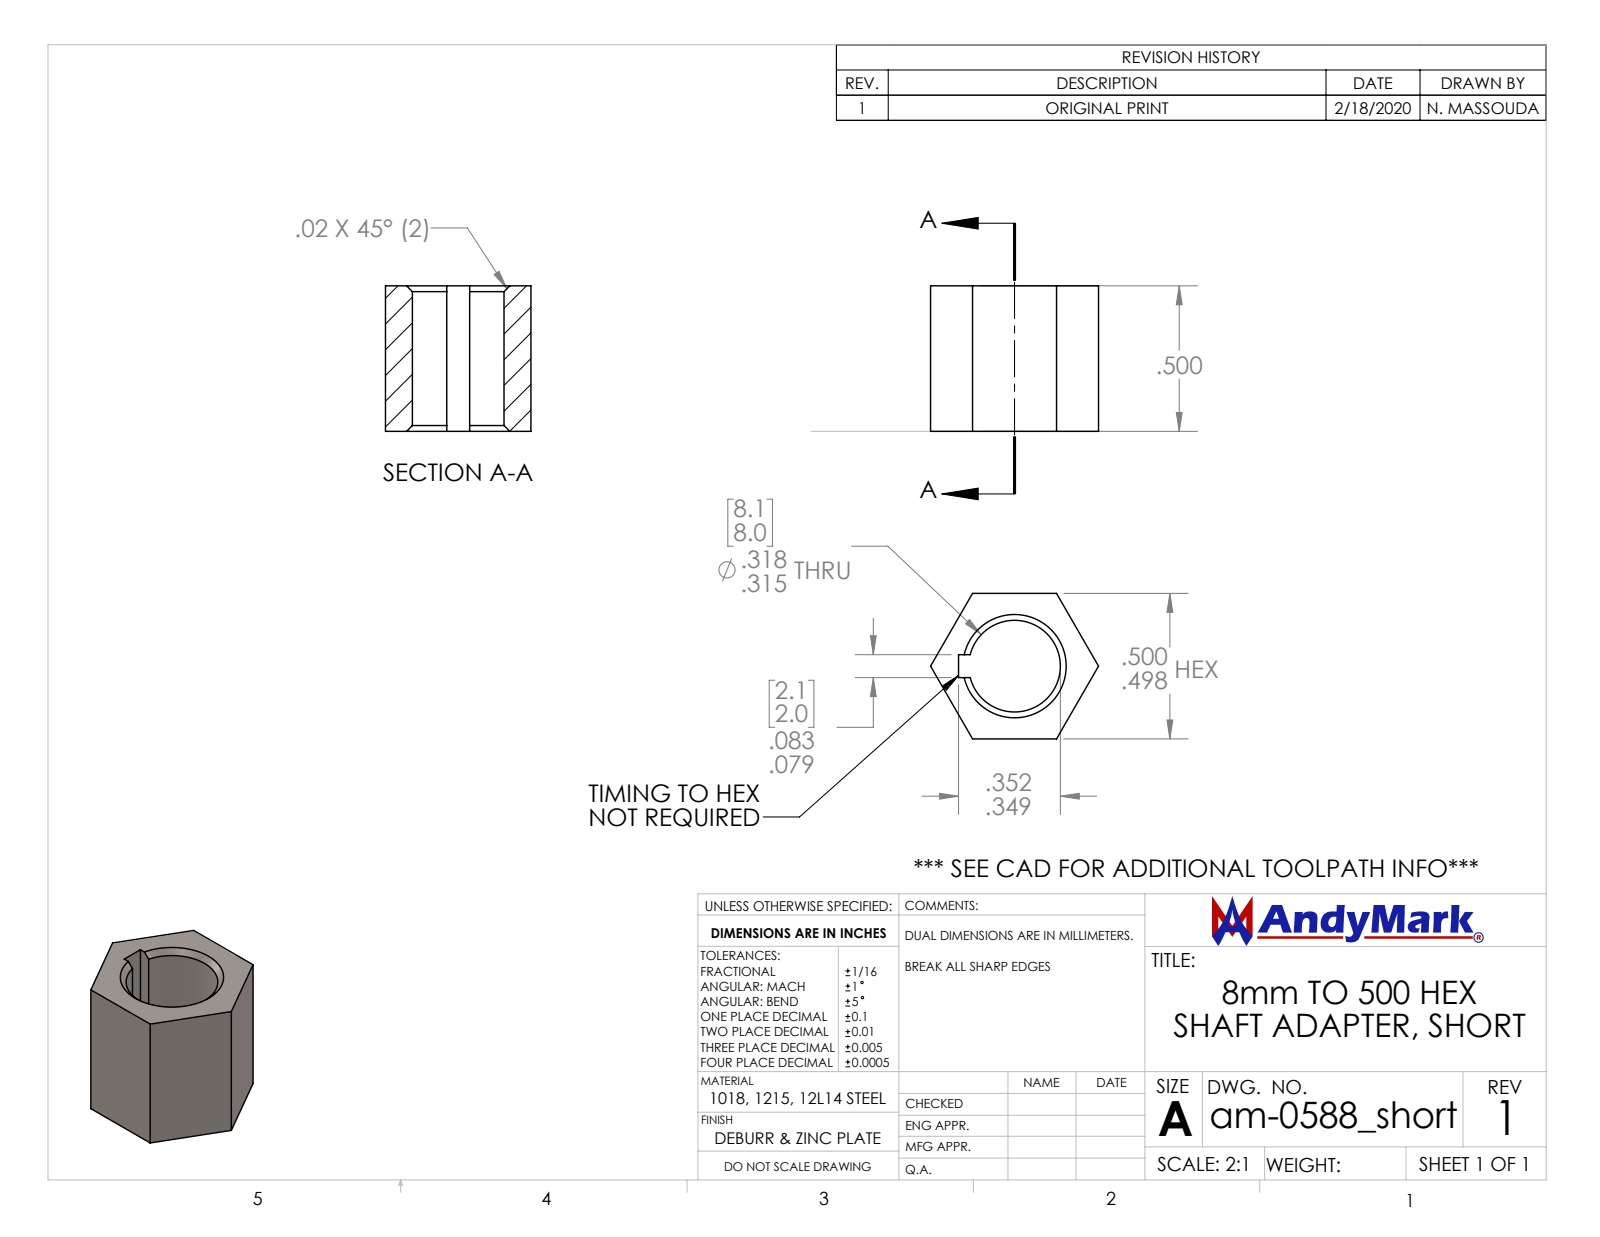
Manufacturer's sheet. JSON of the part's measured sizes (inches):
{"part_name": "am-0588_short 8mm 500 Hex Adapter Shaft 500 long", "step_written_by": "SolidWorks 2024 (CONFIG_CONTROL_DESIGN)", "units": "inches", "bodies": {"solids": 1, "faces": 32, "planar": 11, "cylindrical": 3, "other": 18}, "overall_size": [0.577, 0.5, 0.5], "volume_in3": 0.067, "surface_area_in2": 1.621, "round_holes": [[0.315, 1]], "face_to_face_distances": [0.5, 0.211, 0.289, 0.079]}
